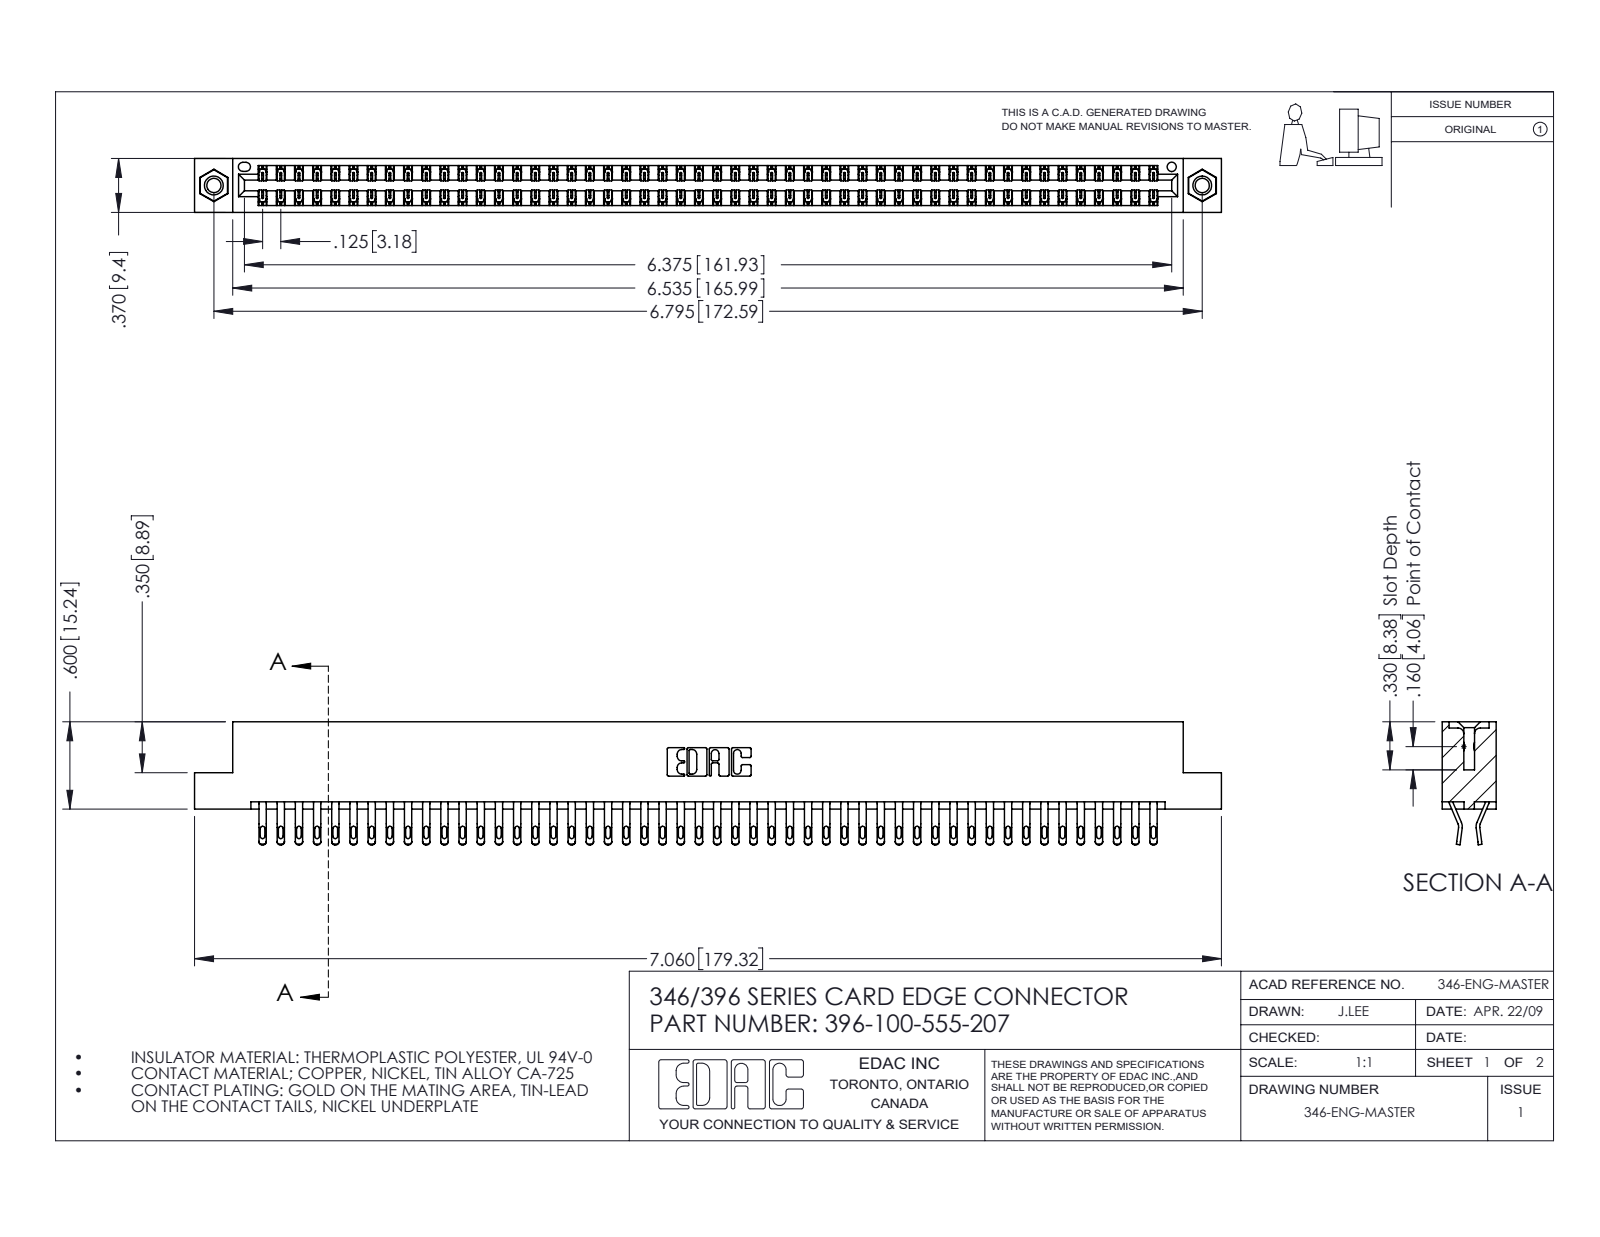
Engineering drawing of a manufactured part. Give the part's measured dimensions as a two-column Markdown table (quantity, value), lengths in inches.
| quantity | value |
| --- | --- |
| part name | 346 Part_Flush Mounting Lugs - 0.156 Dia-TI; 396-100-555-207; 345-250-001_345-250-005-103; 345-292-001_555 Tail |
| STEP written by | SolidWorks 2016 (CONFIG_CONTROL_DESIGN) |
| units | inches |
| bodies | 103 solids, 5982 faces (3408 planar, 2558 cylindrical, 16 other) |
| overall size | 7.06 × 0.845 × 0.37 |
| volume | 1.088 in³ |
| surface area | 39.83 in² |
| round holes (diameter × count) | 0.098 × 2, 0.125 × 2, 0.156 × 2, 0.064 × 1 |
| round bosses / shafts (diameter × count) | 0.155 × 2 |
| partial cylindrical surfaces (radius × count) | 0.016 × 200, 0.02 × 200, 0.006 × 150, 0.01 × 22, 0.007 × 6, 0.031 × 6, 0.026 × 3, 0.01 × 2 |
| main face-to-face distances | 0.048, 0.322, 0.37, 0.25, 0.025, 0.072, 0.298, 0.275, 0.148, 0.222 |
| hole center spacings | 0.246, 6.586, 6.795 |
